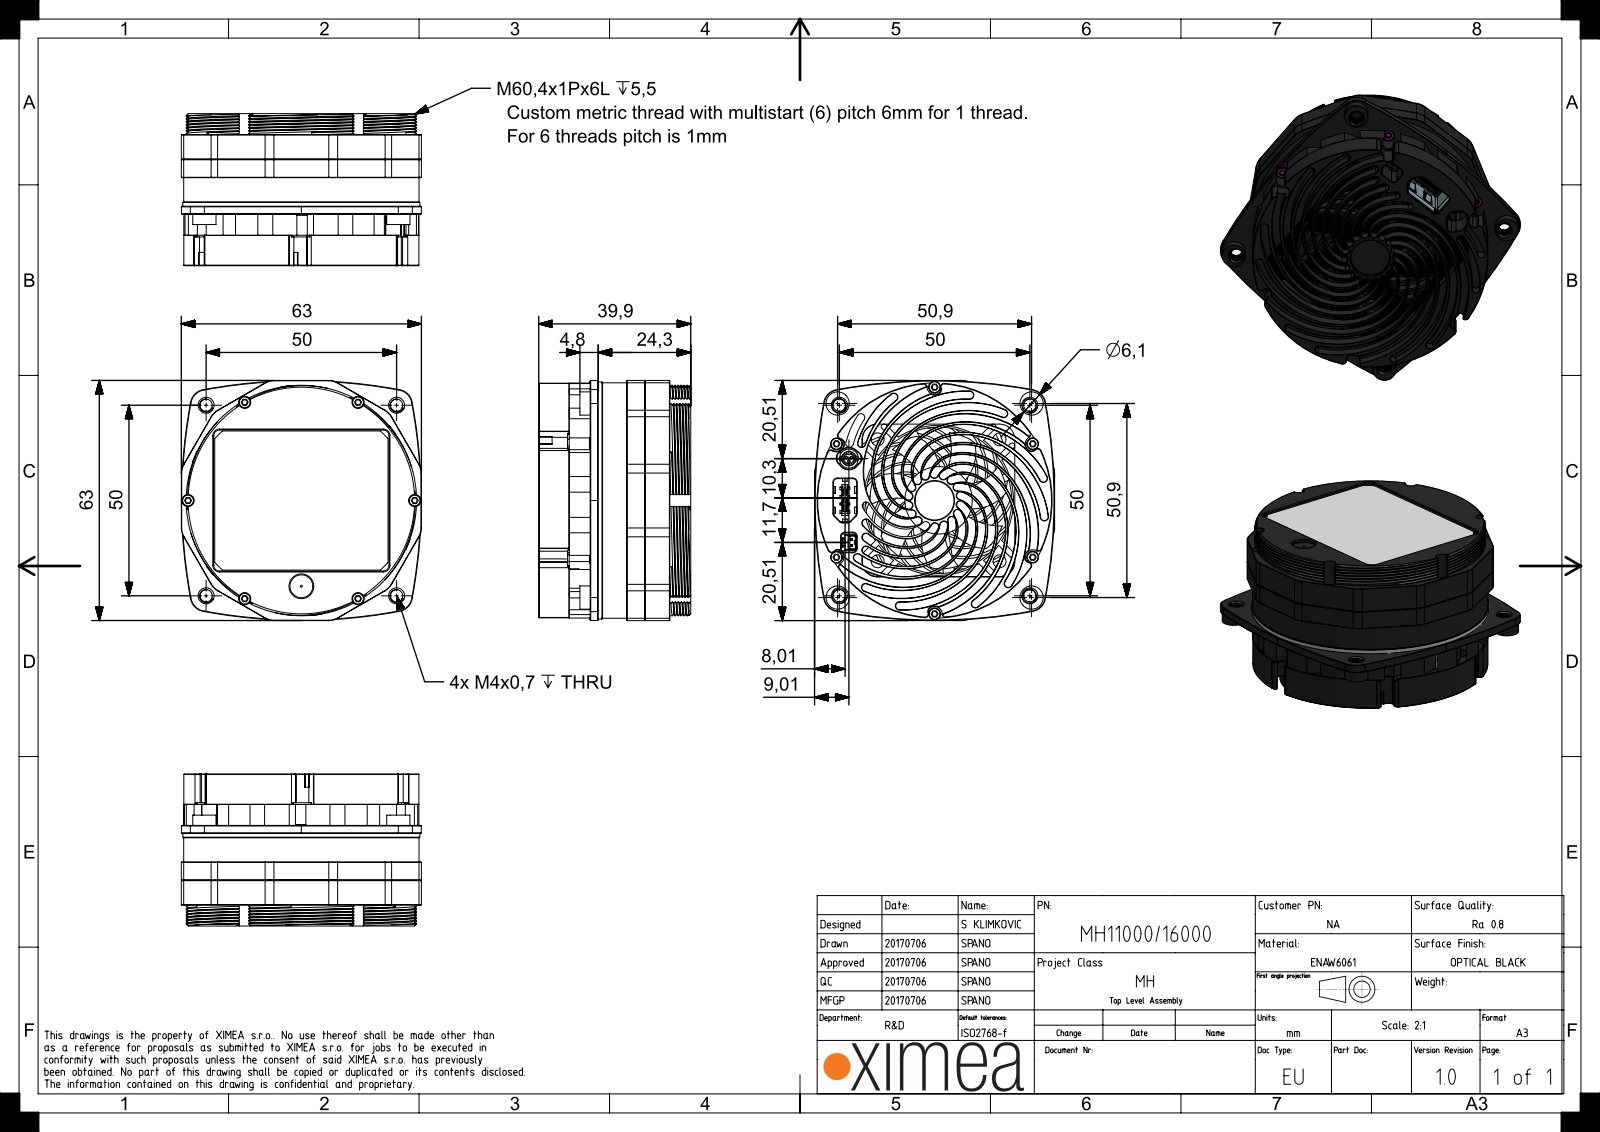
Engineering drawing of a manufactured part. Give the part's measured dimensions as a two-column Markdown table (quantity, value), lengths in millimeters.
| quantity | value |
| --- | --- |
| part name | fan-core; fan-frame; glass-front; FHC (+8 more) |
| STEP written by | SIEMENS PLM Software NX 11.0 (AUTOMOTIVE_DESIGN) |
| units | millimeters |
| bodies | 81 solids, 3192 faces (1219 planar, 1189 cylindrical, 784 other) |
| overall size | 63.02 × 63.02 × 39.9 |
| volume | 55 172 mm³ |
| surface area | 81 064 mm² |
| round holes (diameter × count) | 1.3 × 18, 1.6 × 12, 3.2 × 10, 1.36 × 6, 3 × 4, 3.4 × 4, 4 × 4, 0.51 × 3, 2.4 × 2, 0.5 × 1, 3.8 × 1, 6 × 1 |
| round bosses / shafts (diameter × count) | 0.46 × 40, 2.95 × 12, 6.1 × 4, 61.77 × 1, 61.7 × 1, 60.6 × 1, 60.47 × 1, 39.35 × 1 |
| partial cylindrical surfaces (radius × count) | 1 × 173, 0.2 × 155, 0.3 × 85, 0.5 × 52, 0.4 × 45, 3 × 37, 0.99 × 24, 0.8 × 18 |
| main face-to-face distances | 1, 4.5, 3.5, 16.1, 4.3, 8.8, 5.5, 20.6, 2.2, 11.8 |
| hole center spacings | 28.4, 41.13, 15.11, 29.1, 50.36, 56.17, 15.4, 29.74 |
